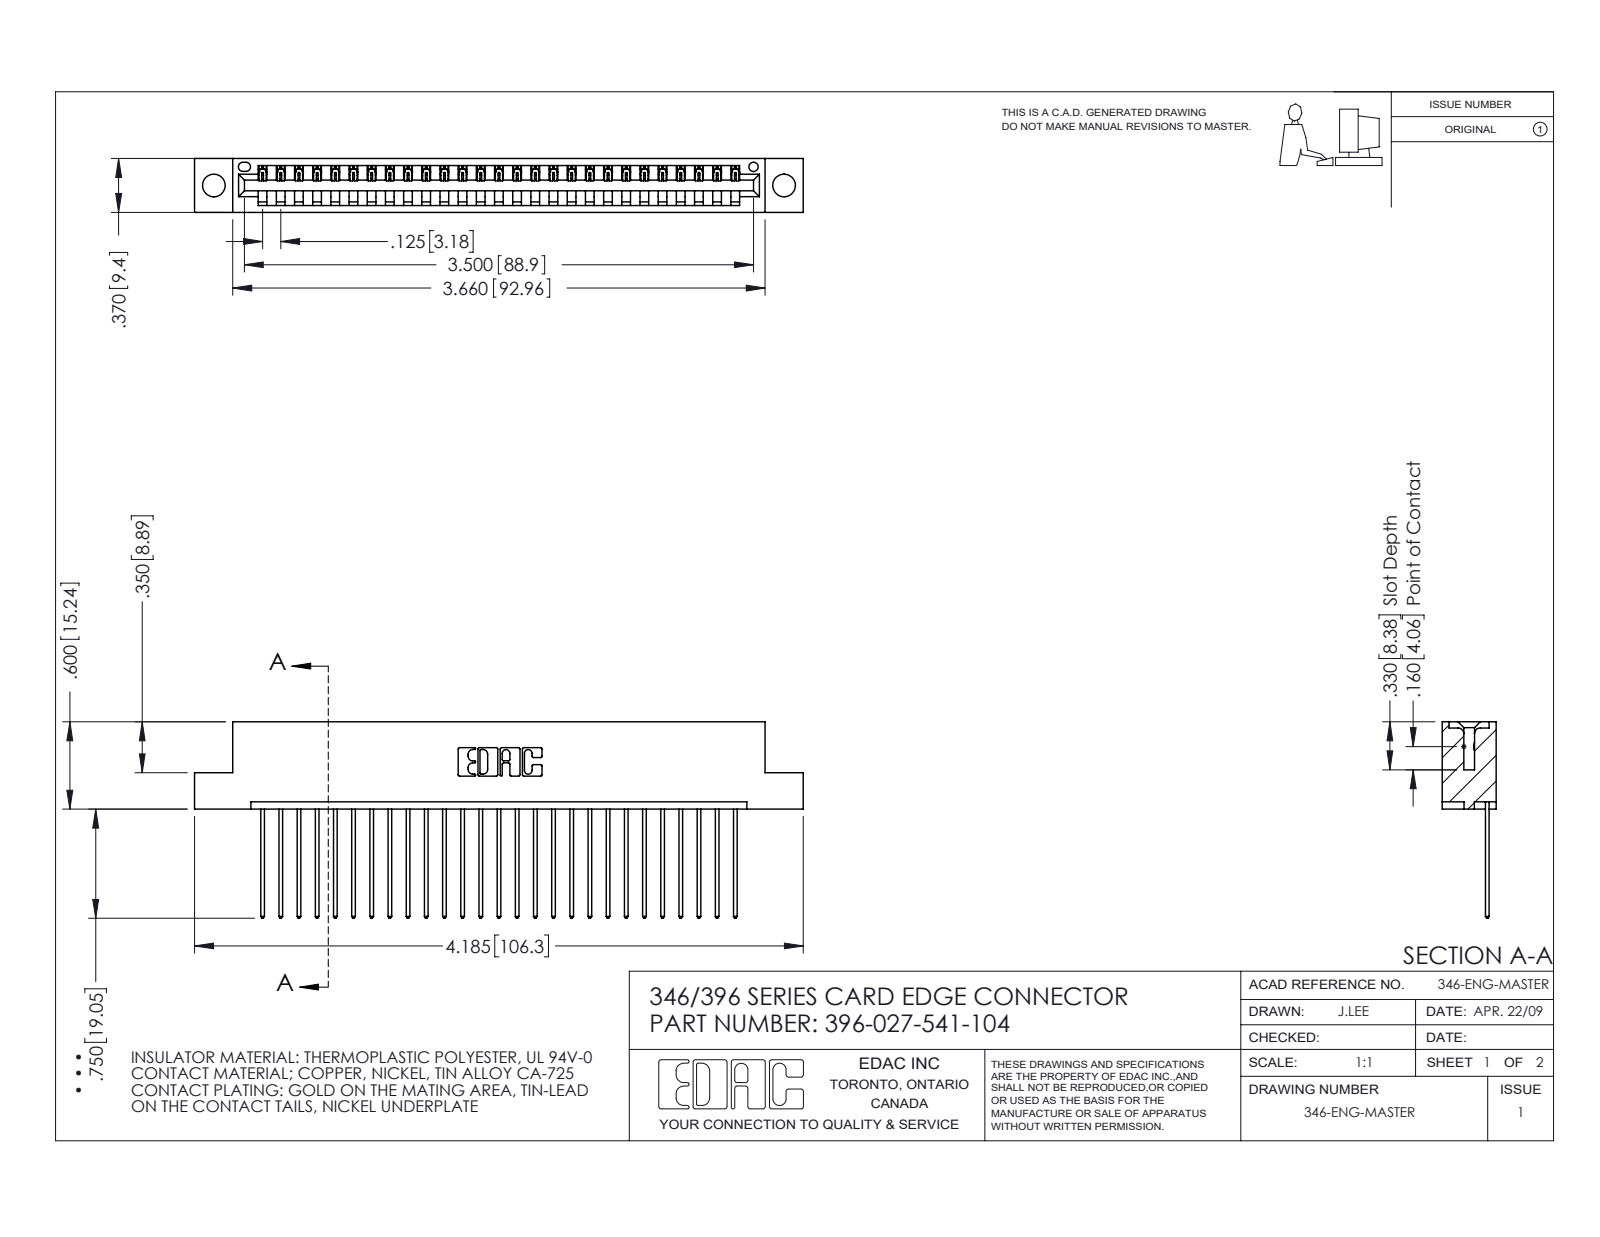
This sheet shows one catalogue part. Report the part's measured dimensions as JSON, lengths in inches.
{"part_name": "346 Part_Flush Mounting Lugs - 0.156 Dia-TH; 396-027-541-104; 345-292-001_345-293-141", "step_written_by": "SolidWorks 2016 (CONFIG_CONTROL_DESIGN)", "units": "inches", "bodies": {"solids": 28, "faces": 1688, "planar": 1156, "cylindrical": 532, "other": 0}, "overall_size": [4.185, 1.35, 0.37], "volume_in3": 0.615, "surface_area_in2": 19.79, "round_holes": [[0.156, 2], [0.064, 1]], "partial_cylinders_radius": [[0.006, 54], [0.01, 54], [0.01, 22], [0.007, 6], [0.031, 6], [0.026, 3], [0.031, 2], [0.04, 2]], "face_to_face_distances": [0.048, 0.322, 0.25, 0.37, 0.072, 0.298, 0.025, 0.148, 0.222, 0.1], "hole_center_spacings": [0.246, 3.712, 3.92]}
